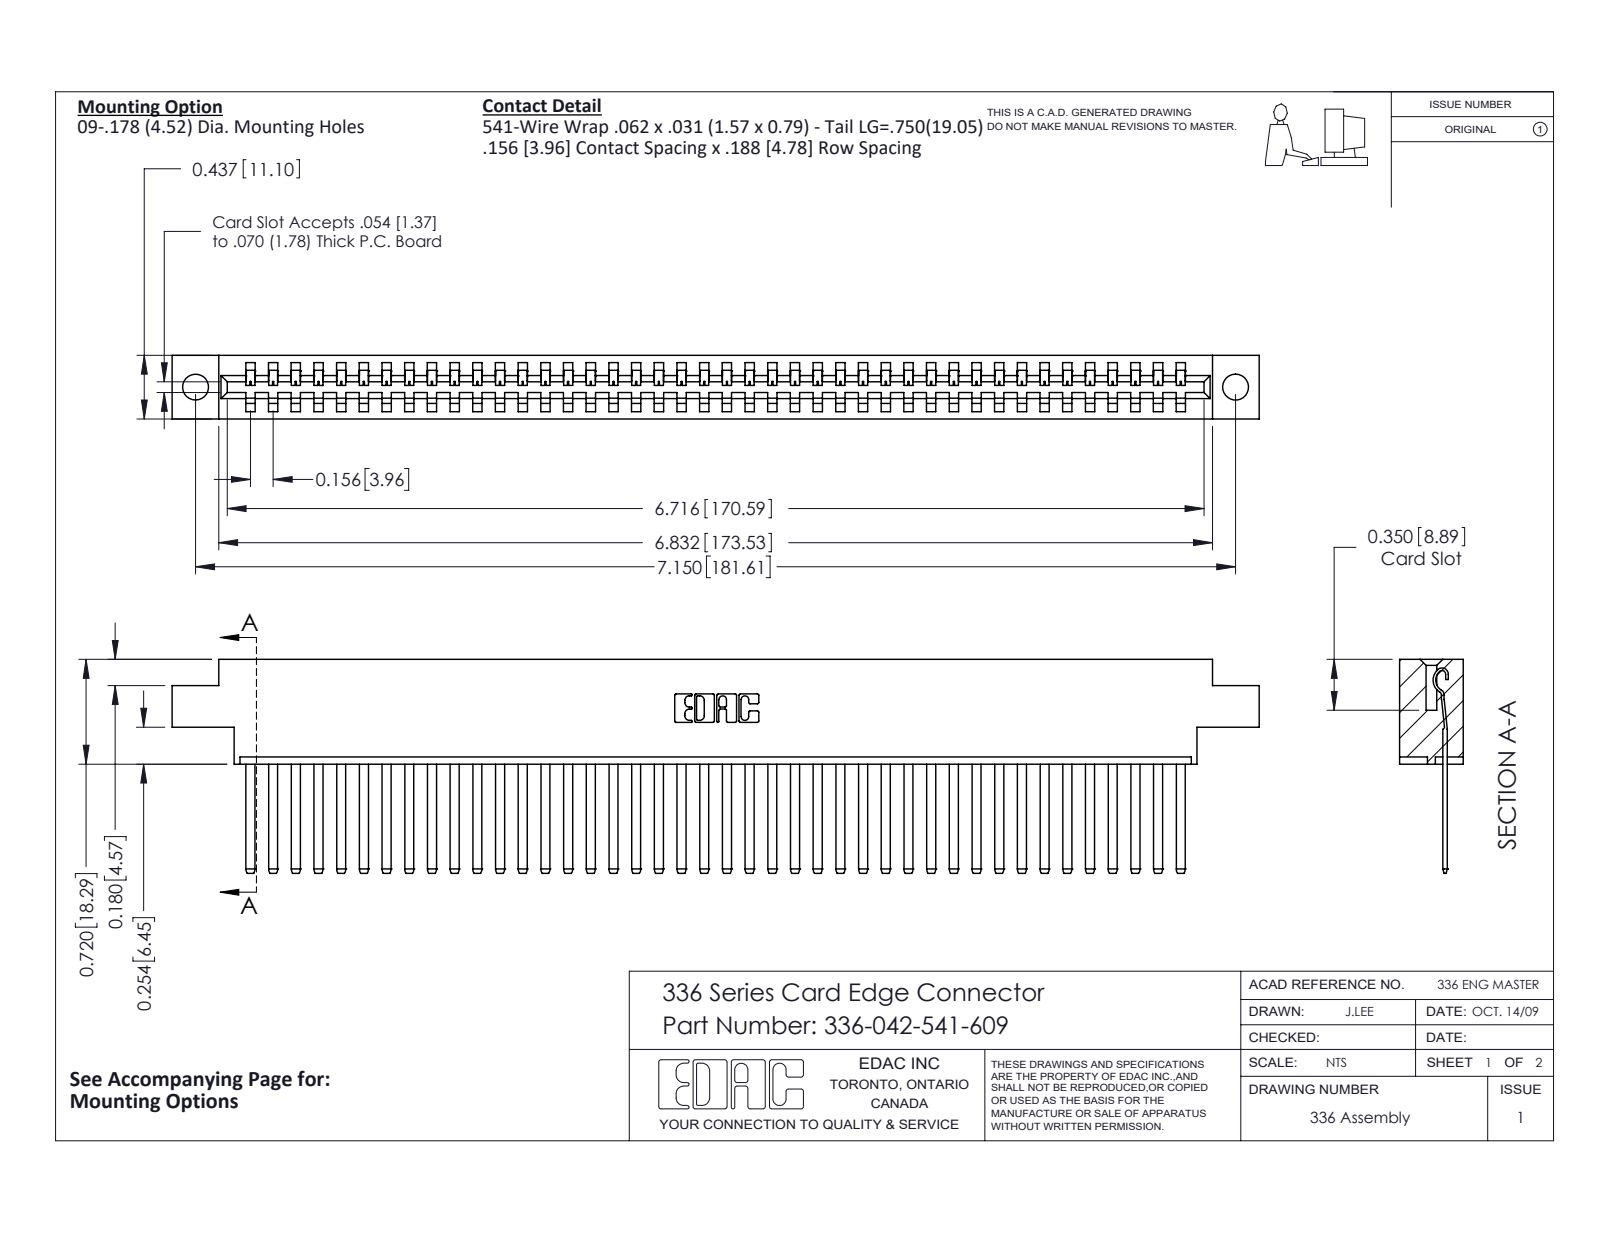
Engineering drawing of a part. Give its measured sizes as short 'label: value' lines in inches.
name: 336 Part_Offset - .178 Dia - TH; 336-290-001_336-290-541; 336-042-541-609
written by: SolidWorks 2020 (CONFIG_CONTROL_DESIGN)
unit: in
bodies: 43 solids, 2218 faces (1502 planar, 716 cylindrical, 0 other)
size: 7.473 × 1.47 × 0.437
volume: 1.679 in³; area: 46.34 in²
holes: 2× ⌀0.178
rounds: 84× R0.004, 84× R0.056, 22× R0.01, 6× R0.007, 6× R0.031, 3× R0.026, 2× R0.022, 2× R0.04
face distances: 0.437, 0.181, 0.328, 0.14, 0.297, 0.109, 0.031, 0.256, 0.05, 0.387
hole spacings: 7.15
